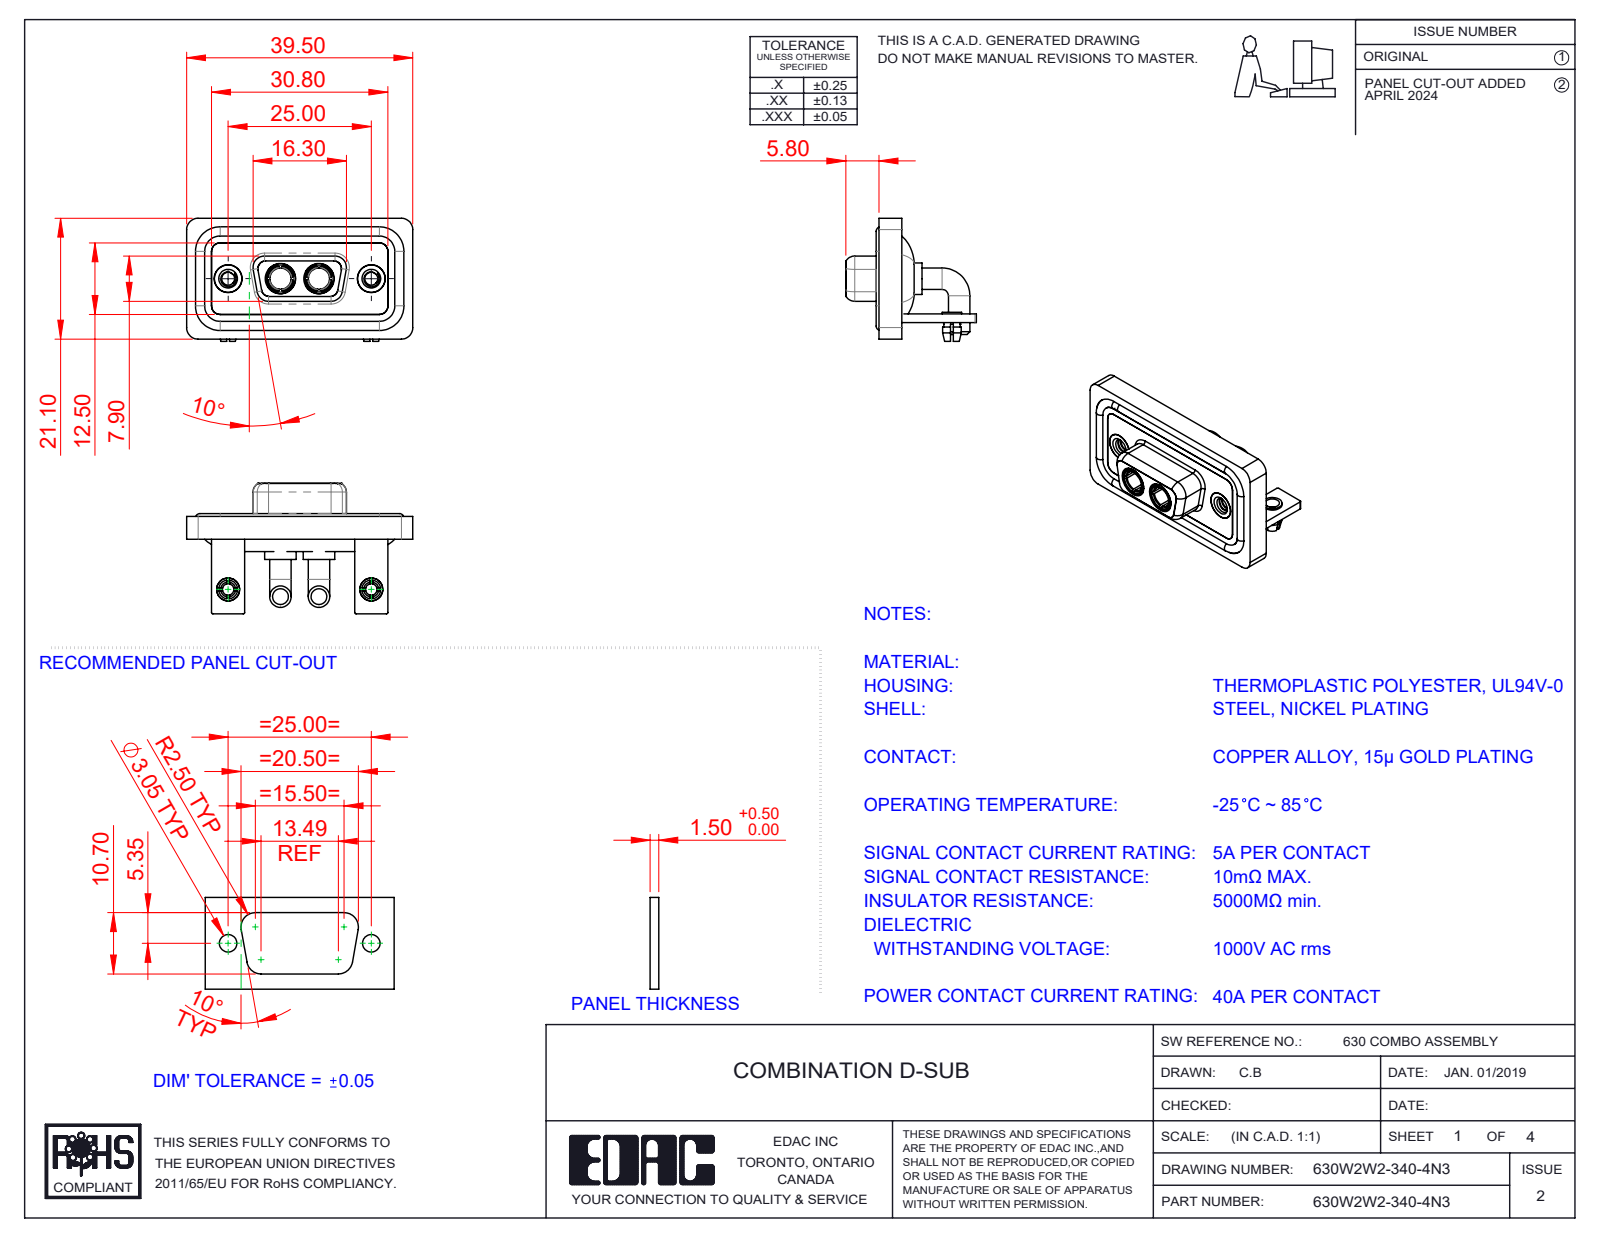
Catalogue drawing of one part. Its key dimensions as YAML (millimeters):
part_name: "630Combo Stabilizer Bracket_50 Contacts; 630Combo Board Lock_50 Contacts; 630Combo Shell Front_09 Contacts; Power Socket_40A RA (+5 more)"
step_written_by: "SolidWorks 2023 (CONFIG_CONTROL_DESIGN)"
units: millimeters
bodies: {solids: 15, faces: 682, planar: 231, cylindrical: 294, other: 157}
overall_size: [39.5, 22.8, 21.5]
volume: 5364
surface_area: 8819
round_holes:
  - {diameter: 4.85, count: 4}
  - {diameter: 2, count: 2}
  - {diameter: 2.26, count: 2}
  - {diameter: 2.5, count: 2}
  - {diameter: 3.2, count: 2}
  - {diameter: 3.7, count: 2}
  - {diameter: 4, count: 2}
  - {diameter: 4.05, count: 2}
  - {diameter: 5, count: 2}
  - {diameter: 5.3, count: 2}
round_bosses_or_shafts:
  - {diameter: 3.75, count: 4}
  - {diameter: 1.6, count: 4}
  - {diameter: 5.5, count: 2}
  - {diameter: 5.2, count: 2}
  - {diameter: 4.96, count: 2}
  - {diameter: 4.95, count: 2}
  - {diameter: 4.8, count: 2}
  - {diameter: 4.75, count: 2}
partial_cylinders:
  - {radius: 2, count: 19}
  - {radius: 1.5, count: 18}
  - {radius: 0.25, count: 16}
  - {radius: 1.35, count: 8}
  - {radius: 1.6, count: 8}
  - {radius: 0.5, count: 5}
  - {radius: 0.6, count: 4}
  - {radius: 0.65, count: 4}
face_to_face_distances: [0.4, 2.9, 1.5, 1.8, 1.1, 3.7, 0.8, 2.5, 1.6, 3.1]
hole_center_spacings: [9.14, 15.86, 25, 6.72]
